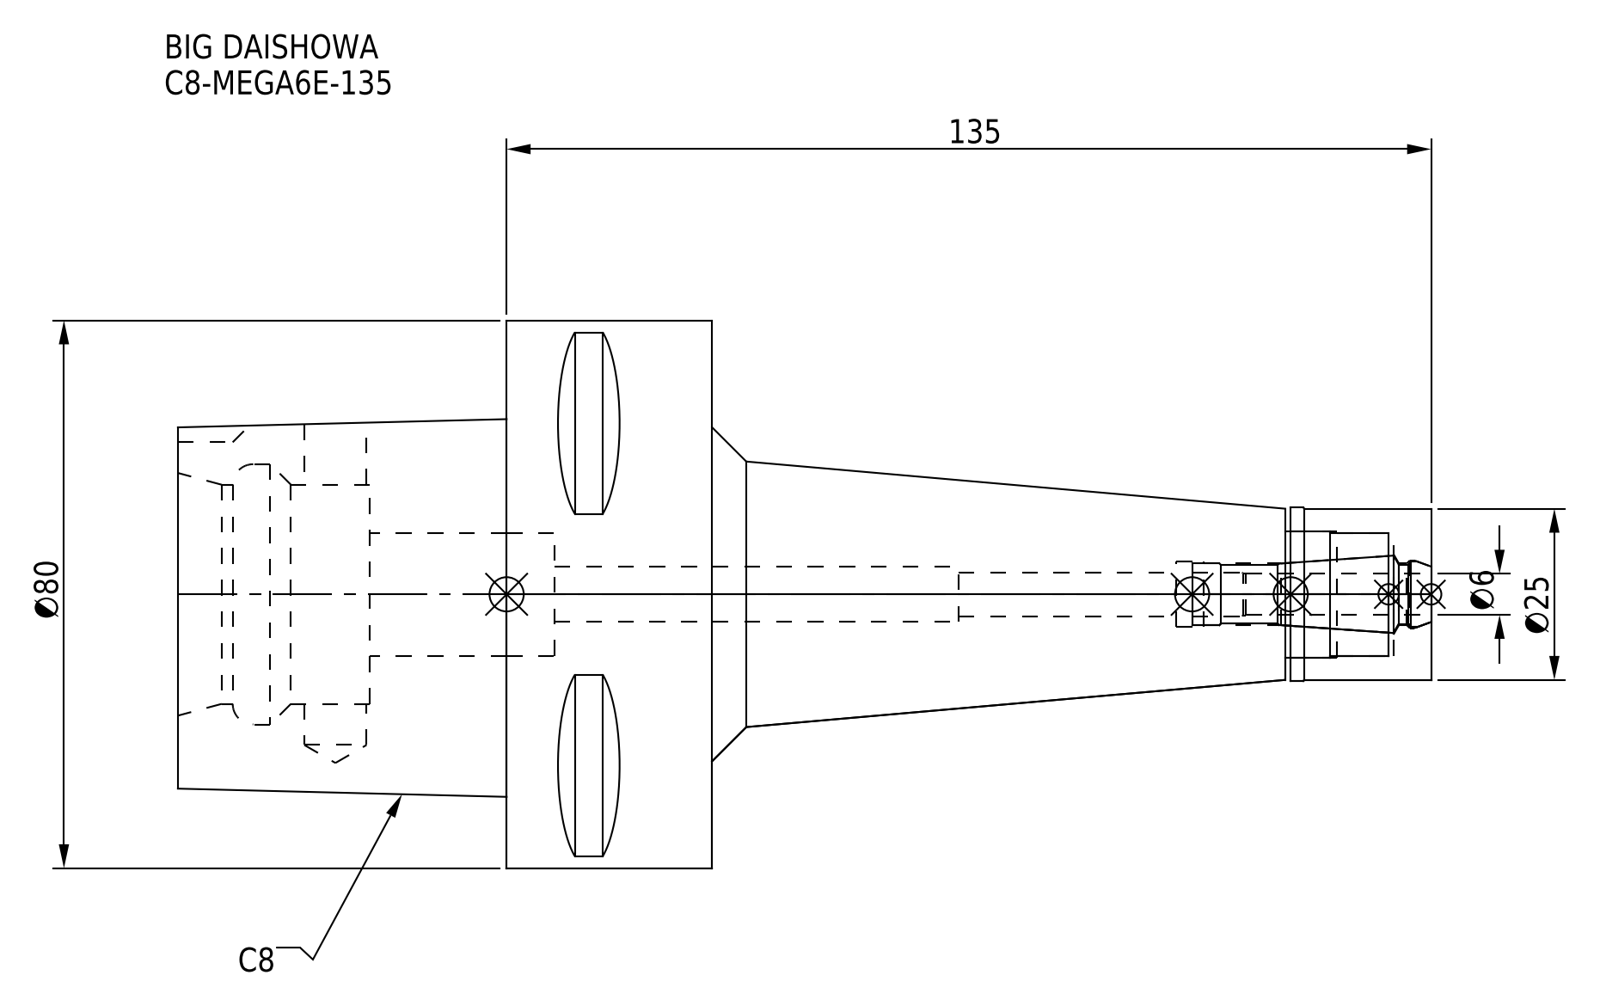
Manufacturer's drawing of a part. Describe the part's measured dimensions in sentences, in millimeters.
The part is named "C8-MEGA6E-135-060_ASM.stp; C8-MEGA6E-135; DXF_TEMP_ASSY_ASM_4_ASM.stp; C8-MEGA6E-135-060.stp (+3 more)". Its 3-D file was written by "SolidWorks 2019 (CONFIG_CONTROL_DESIGN)". It is 2 solids with 100 faces: 37 planar, 39 cylindrical and 24 other. Overall it measures 183 by 80 by 80 millimeters. Its volume is 298 012 cubic millimeters and its surface area 45 891 square millimeters. Round holes: 1 of diameter 6.4, 1 of diameter 8, 1 of diameter 9, 1 of diameter 9.1, 1 of diameter 9.6, 1 of diameter 9.9, 1 of diameter 18, 1 of diameter 18.5, 1 of diameter 32, 1 of diameter 38. Round bosses or shafts: 1 of diameter 80, 1 of diameter 25.3, 1 of diameter 25. Partial cylindrical surfaces (rounded edges, fillets, slot ends): 1 of radius 6. The main face-to-face distances are 30, 78, 48, 20, 50, 28, 105, 135, 155, 183.
